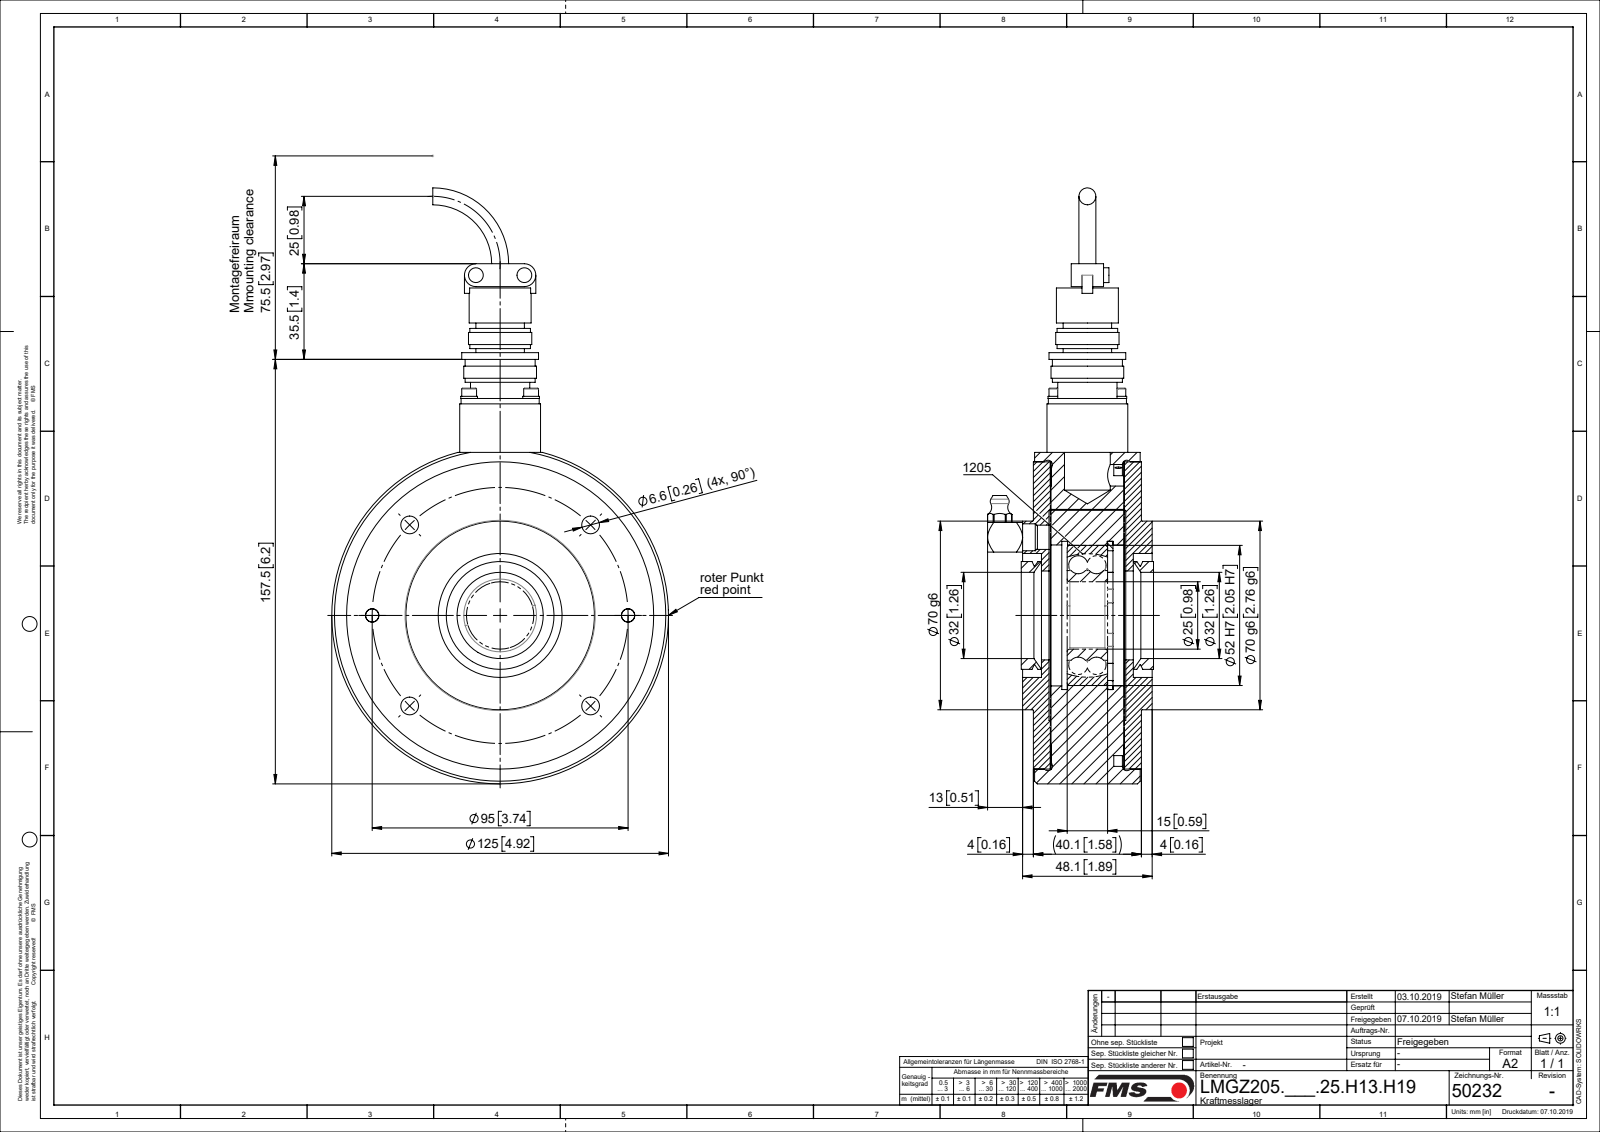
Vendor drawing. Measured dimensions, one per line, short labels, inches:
name: ZEICHNUNG7; L50232; L4832404; L50234 (+8 more)
written by: Mechanical Desktop 2007 (CONFIG_CONTROL_DESIGN)
unit: in
bodies: 22 solids, 450 faces (122 planar, 258 cylindrical, 70 other)
size: 8.707 × 4.921 × 2.465
volume: 29.56 in³; area: 227.9 in²
holes: 6× ⌀0.26, 4× ⌀0.102, 4× ⌀0.126, 4× ⌀0.134, 2× ⌀0.197, 2× ⌀0.433, 1× ⌀0.351, 1× ⌀0.906, 1× ⌀0.984, 1× ⌀1.22, 1× ⌀1.299, 1× ⌀1.492
bosses: 6× ⌀0.217, 4× ⌀0.244, 4× ⌀0.118, 4× ⌀0.098, 3× ⌀0.394, 2× ⌀0.236, 1× ⌀4.921, 1× ⌀4.488
rounds: 8× R0.197, 2× R0.167, 1× R1.594, 1× R1.85
face distances: 1.073, 1.321, 0.248, 0.258, 1.331, 1.063, 1.083, 0.157, 0.415, 1.579
hole spacings: 1.87, 0.64, 0.906, 1.431, 2.645, 3.456, 1.281, 1.335
